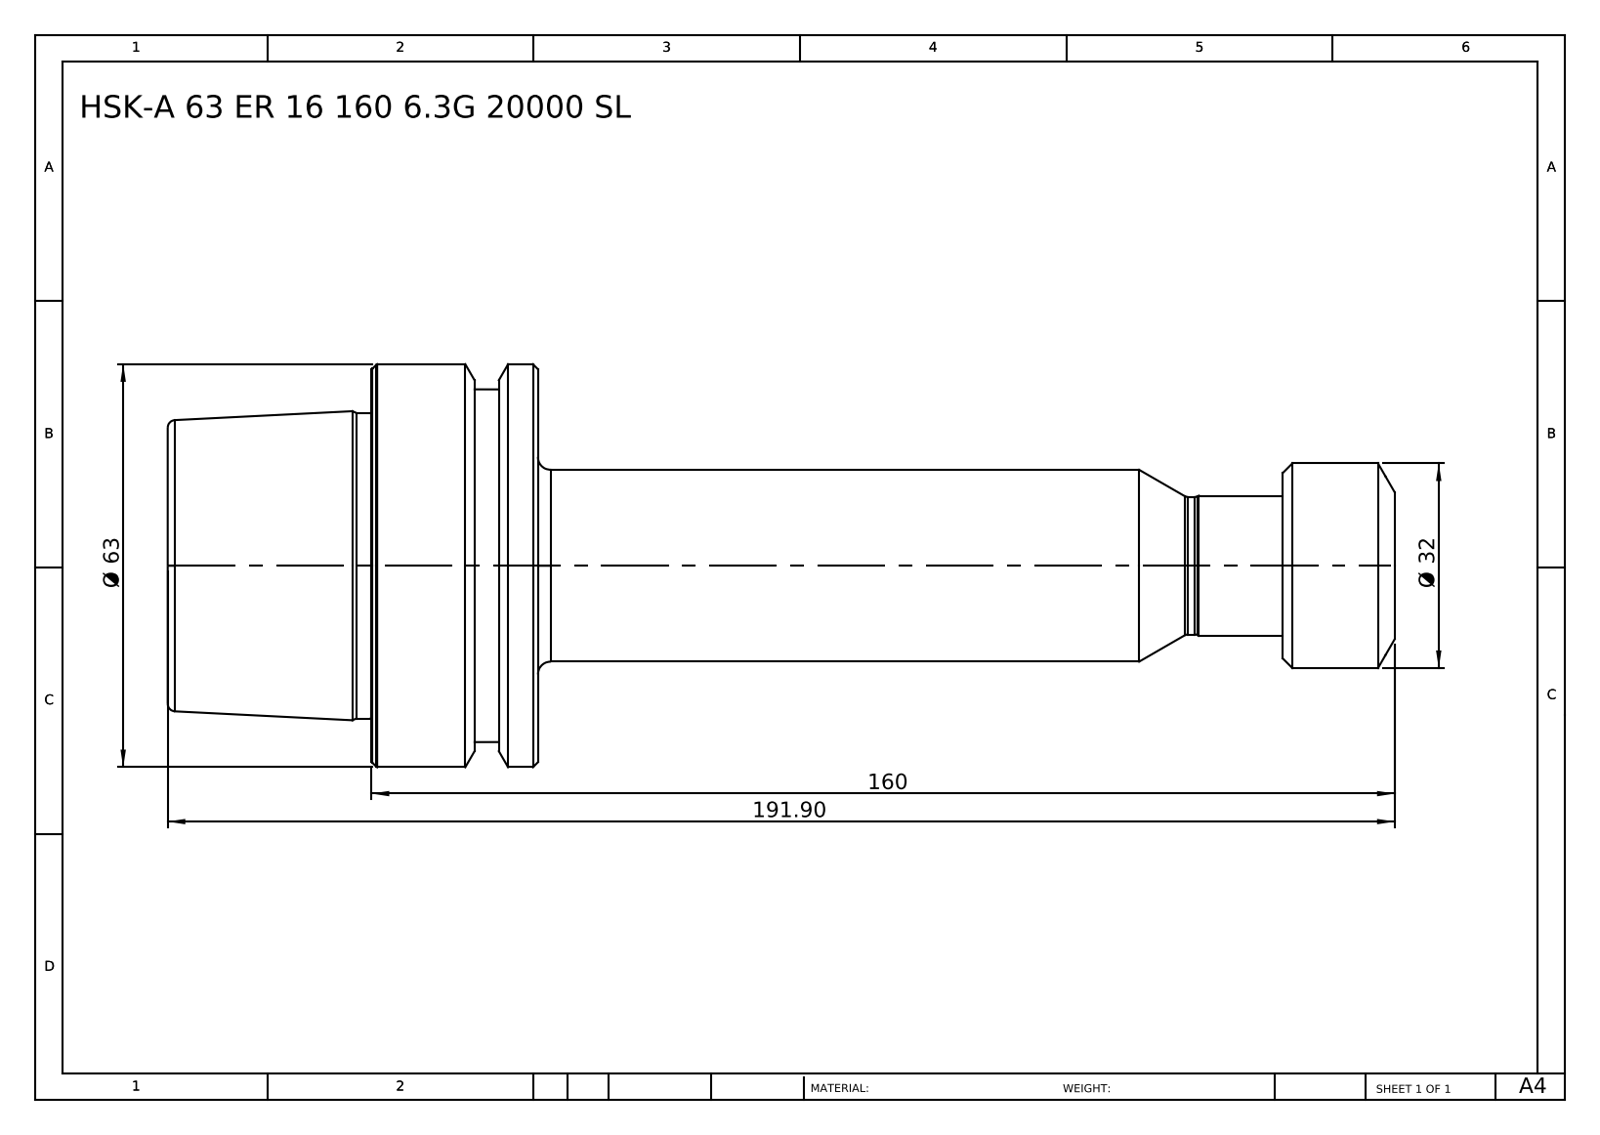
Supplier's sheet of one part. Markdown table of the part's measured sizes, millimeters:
| quantity | value |
| --- | --- |
| part name | HSK-A 63 ER 16 160 6.3G 20000 SL |
| STEP written by | SolidWorks 2014 (CONFIG_CONTROL_DESIGN) |
| units | millimeters |
| bodies | 1 solid, 63 faces (7 planar, 14 cylindrical, 42 other) |
| overall size | 191.9 × 63.03 × 63.03 |
| volume | 222 336 mm³ |
| surface area | 29 127 mm² |
| round bosses / shafts (diameter × count) | 63.03 × 1, 47.78 × 1, 32 × 1, 30 × 1, 21.9 × 1, 21.5 × 1 |
| main face-to-face distances | 57.9, 26, 31.9, 134, 160, 191.9, 17.5, 116.5, 142.5, 174.4 |
